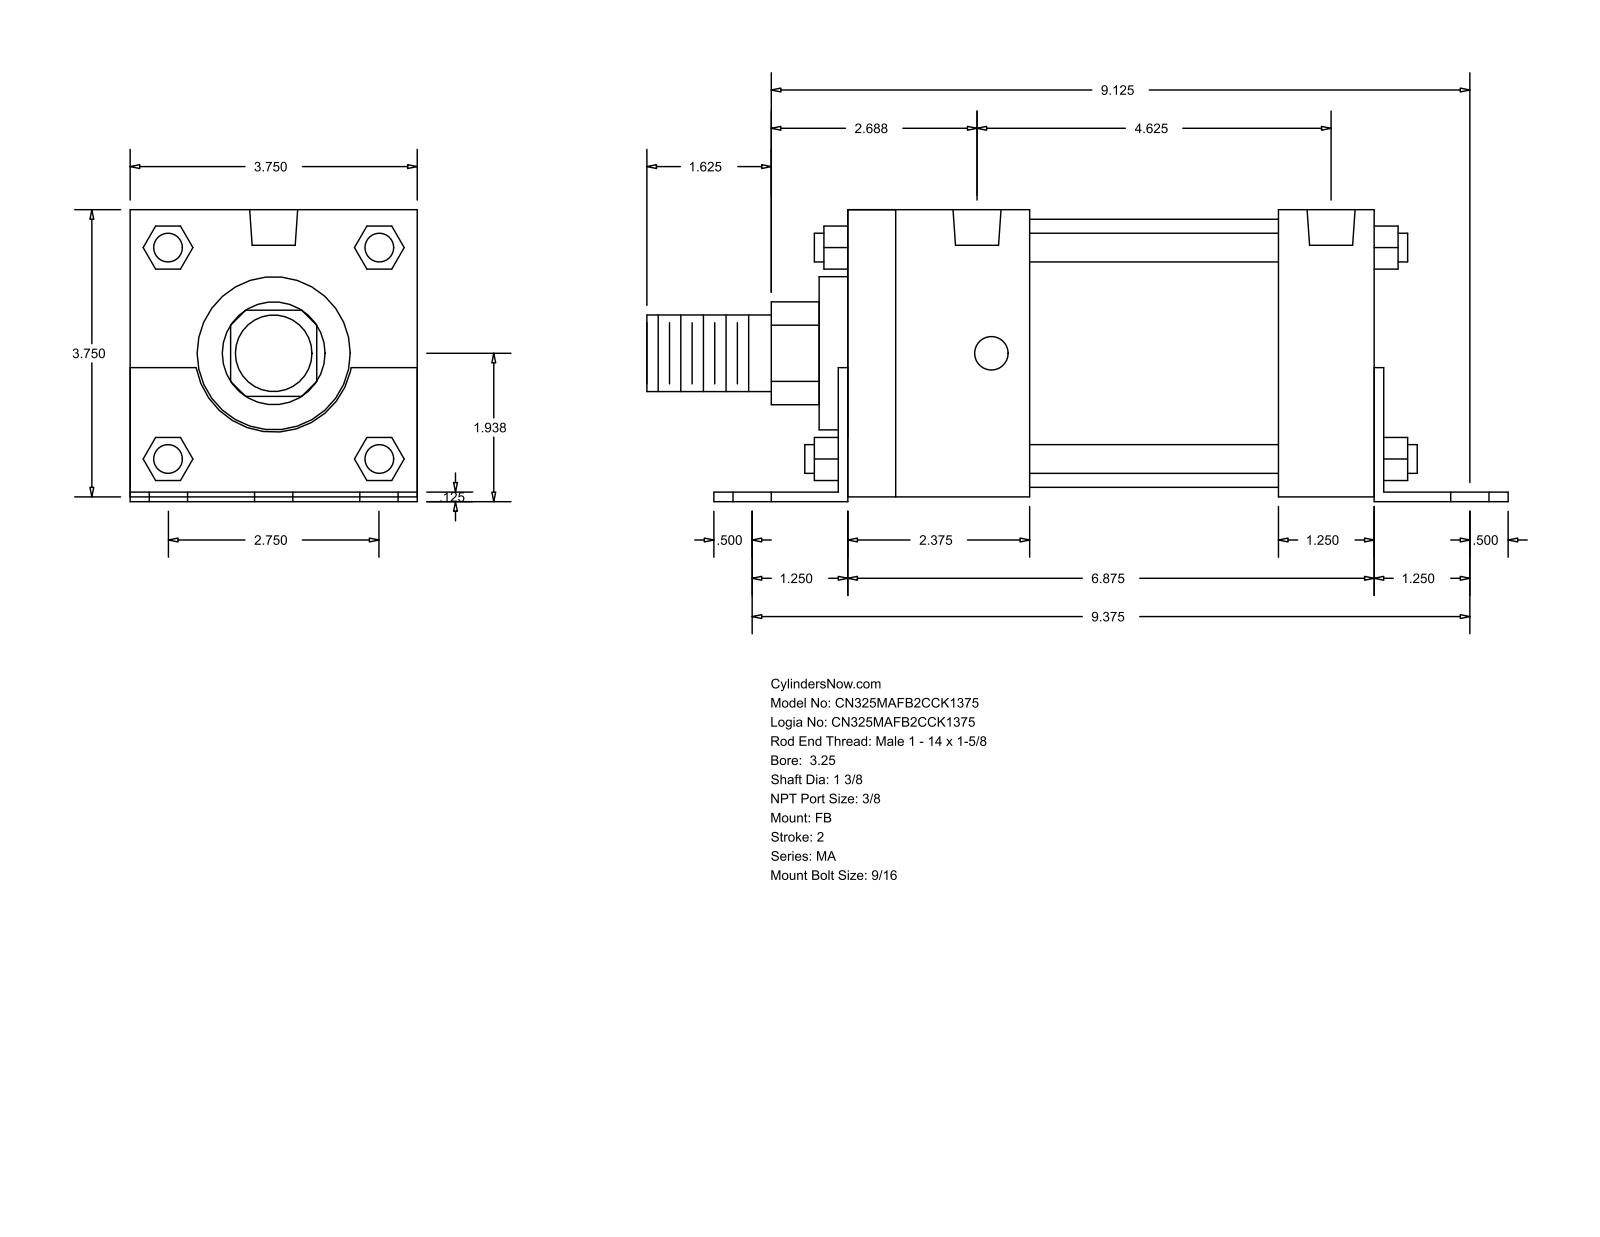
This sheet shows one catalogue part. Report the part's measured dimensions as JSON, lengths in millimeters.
{"part_name": "MA_FB__0325_1.375", "step_written_by": "GSSL Pune (CONFIG_CONTROL_DESIGN)", "units": "millimeters", "bodies": {"solids": 0, "faces": 140, "planar": 105, "cylindrical": 35, "other": 0}, "overall_size": [285.75, 96.84, 95.25], "round_holes": [[14.29, 6], [11.11, 4], [15.93, 2]], "round_bosses_or_shafts": [[9.53, 4], [88.9, 1], [50.8, 1], [34.92, 1], [25.4, 1]], "partial_cylinders_radius": [[17.06, 1], [26.16, 1]], "face_to_face_distances": [95.24, 3.17, 1.59, 96.83, 1.58, 93.66, 177.8, 174.63, 31.75, 34.92], "hole_center_spacings": [34.92, 240.68, 238.13, 4.77, 57.78, 61.65, 69.84, 82.38]}
